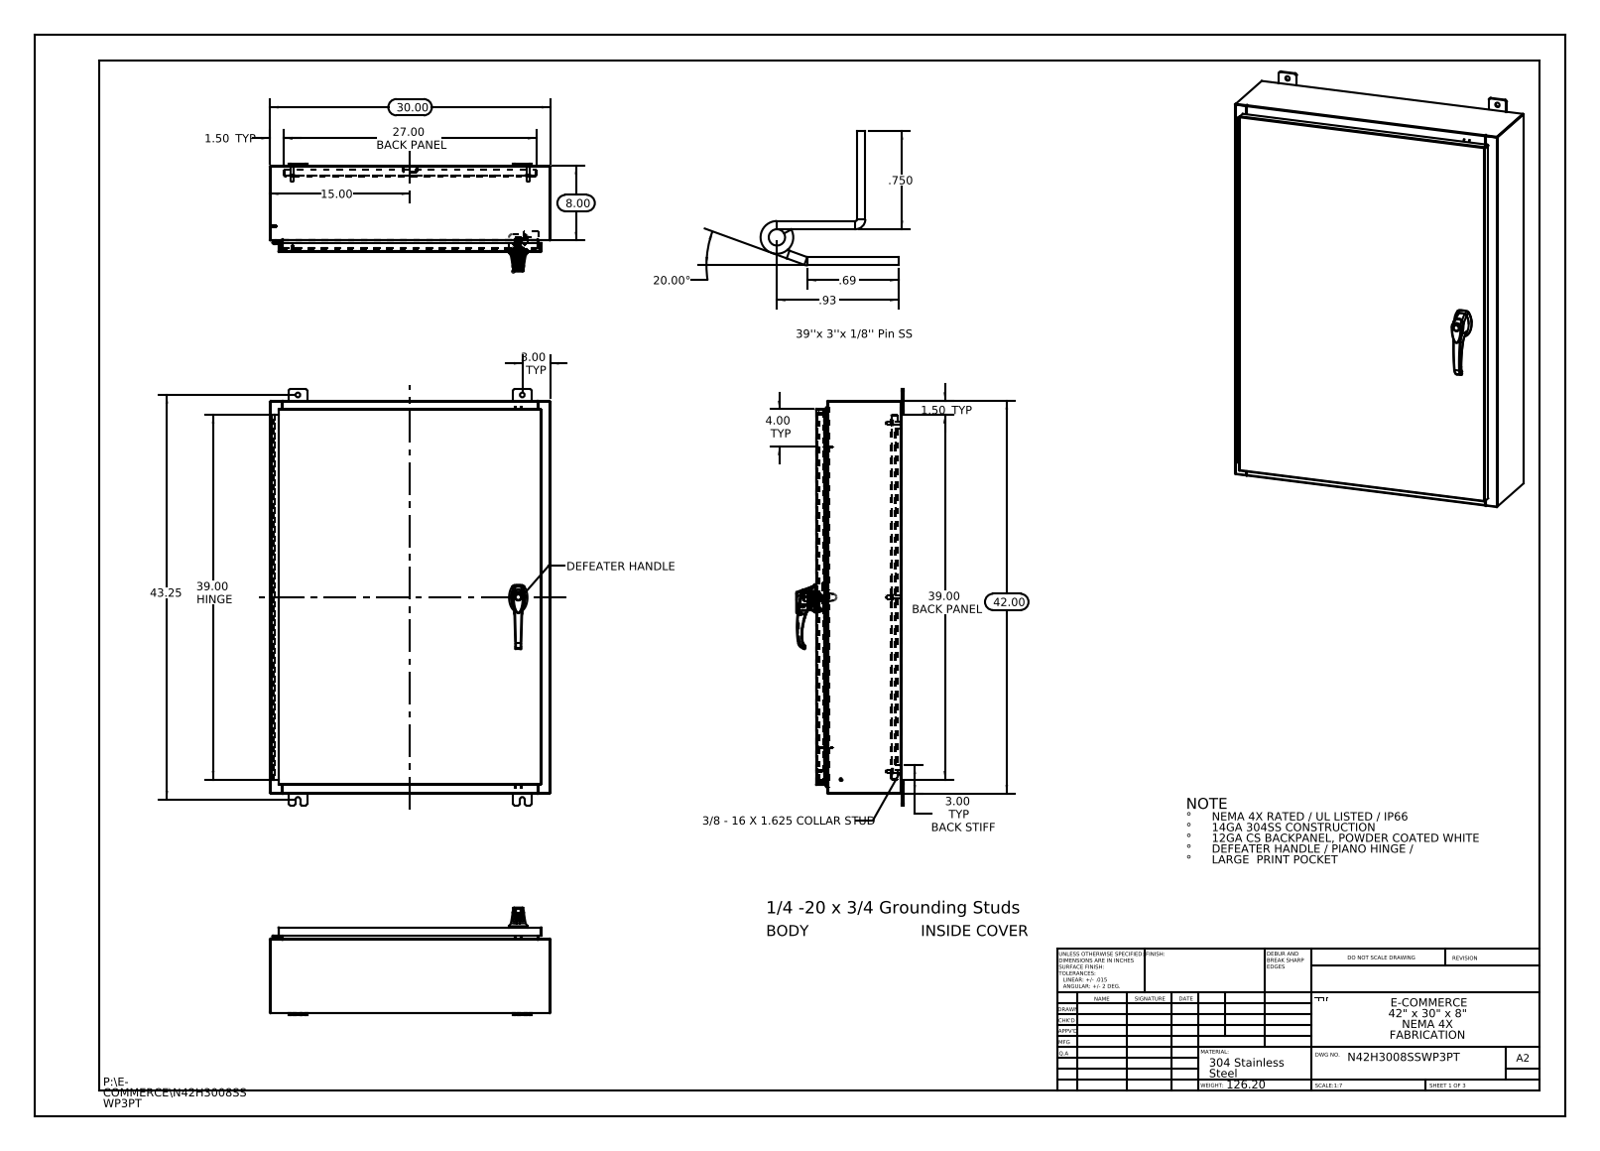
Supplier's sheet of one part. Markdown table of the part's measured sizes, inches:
| quantity | value |
| --- | --- |
| part name | 2616310101; 00005309_G26103101; N42H3008SSWP3PT Top; N42H3008SSWP3PT 263033_Industrilas (+8 more) |
| STEP written by | SolidWorks 2013 (CONFIG_CONTROL_DESIGN) |
| units | inches |
| bodies | 40 solids, 3038 faces (1155 planar, 1165 cylindrical, 718 other) |
| overall size | 44.5 × 30 × 11.495 |
| volume | 446.2 in³ |
| surface area | 11 005 in² |
| round holes (diameter × count) | 0.5 × 10, 0.25 × 4, 0.138 × 3, 0.161 × 3, 0.079 × 2, 0.203 × 2, 0.313 × 2, 0.437 × 2, 0.125 × 1, 0.125 × 1, 0.197 × 1, 0.276 × 1 |
| round bosses / shafts (diameter × count) | 0.625 × 6, 0.375 × 6, 0.33 × 6, 0.157 × 4, 0.14 × 4, 0.315 × 3, 0.236 × 3, 1.181 × 1 |
| partial cylindrical surfaces (radius × count) | 0.118 × 37, 0.006 × 33, 0.013 × 28, 0.19 × 24, 0.088 × 22, 0.039 × 15, 0.028 × 12, 0.008 × 6 |
| main face-to-face distances | 0.075, 9.126, 9.051, 0.104, 9.201, 1, 8.126, 1.075, 8.051, 1.179 |
| hole center spacings | 14.36, 16.667, 18.625, 31.376, 25.25, 0.295, 0.625, 0.841 |
